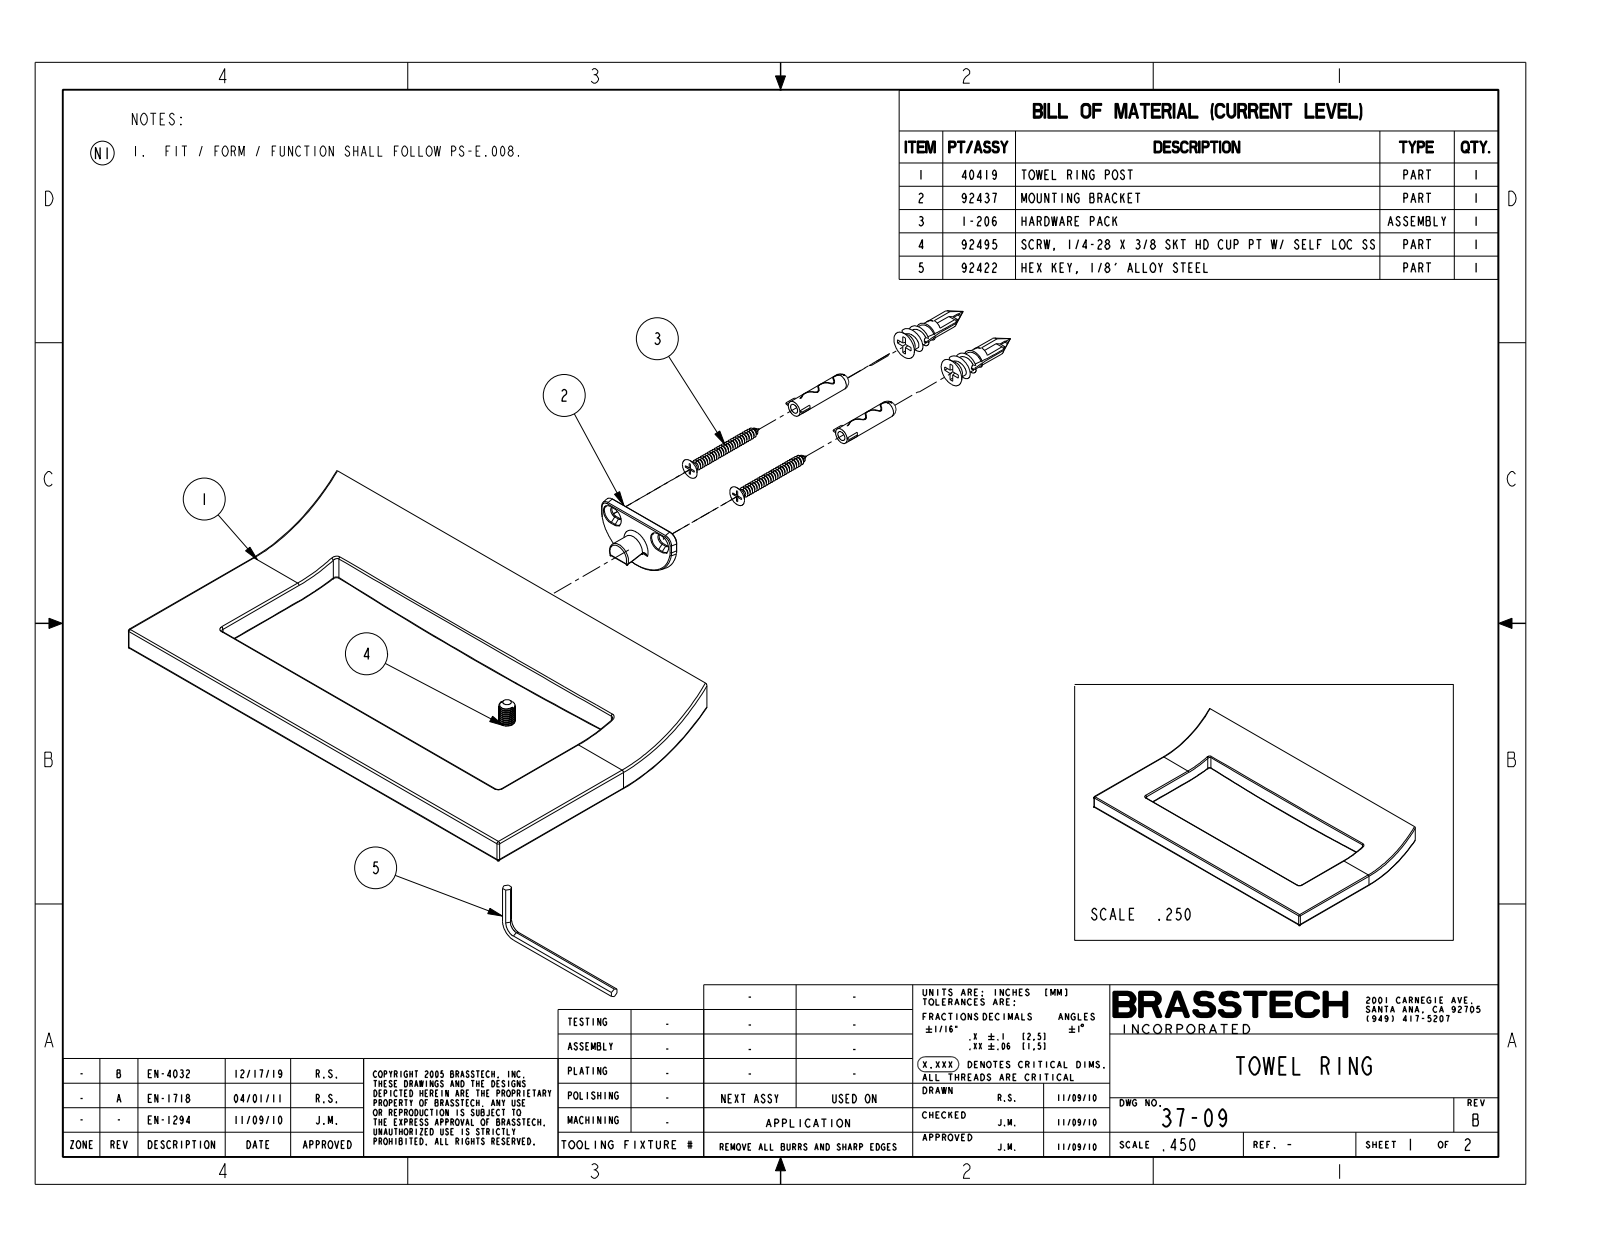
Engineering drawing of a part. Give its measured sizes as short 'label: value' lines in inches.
name: 37-09_WEB
written by: PRO/ENGINEER BY PARAMETRIC TECHNOLOGY CORPORATION, 2009300 (CONFIG_CONTROL_DESIGN)
unit: in
bodies: 0 solids, 36 faces (11 planar, 0 cylindrical, 25 other)
size: 8 × 4.515 × 1.08
face distances: 3.5, 1, 4.397, 0.897, 0.103, 4.5, 3.397, 2.5, 0.015, 0.118
